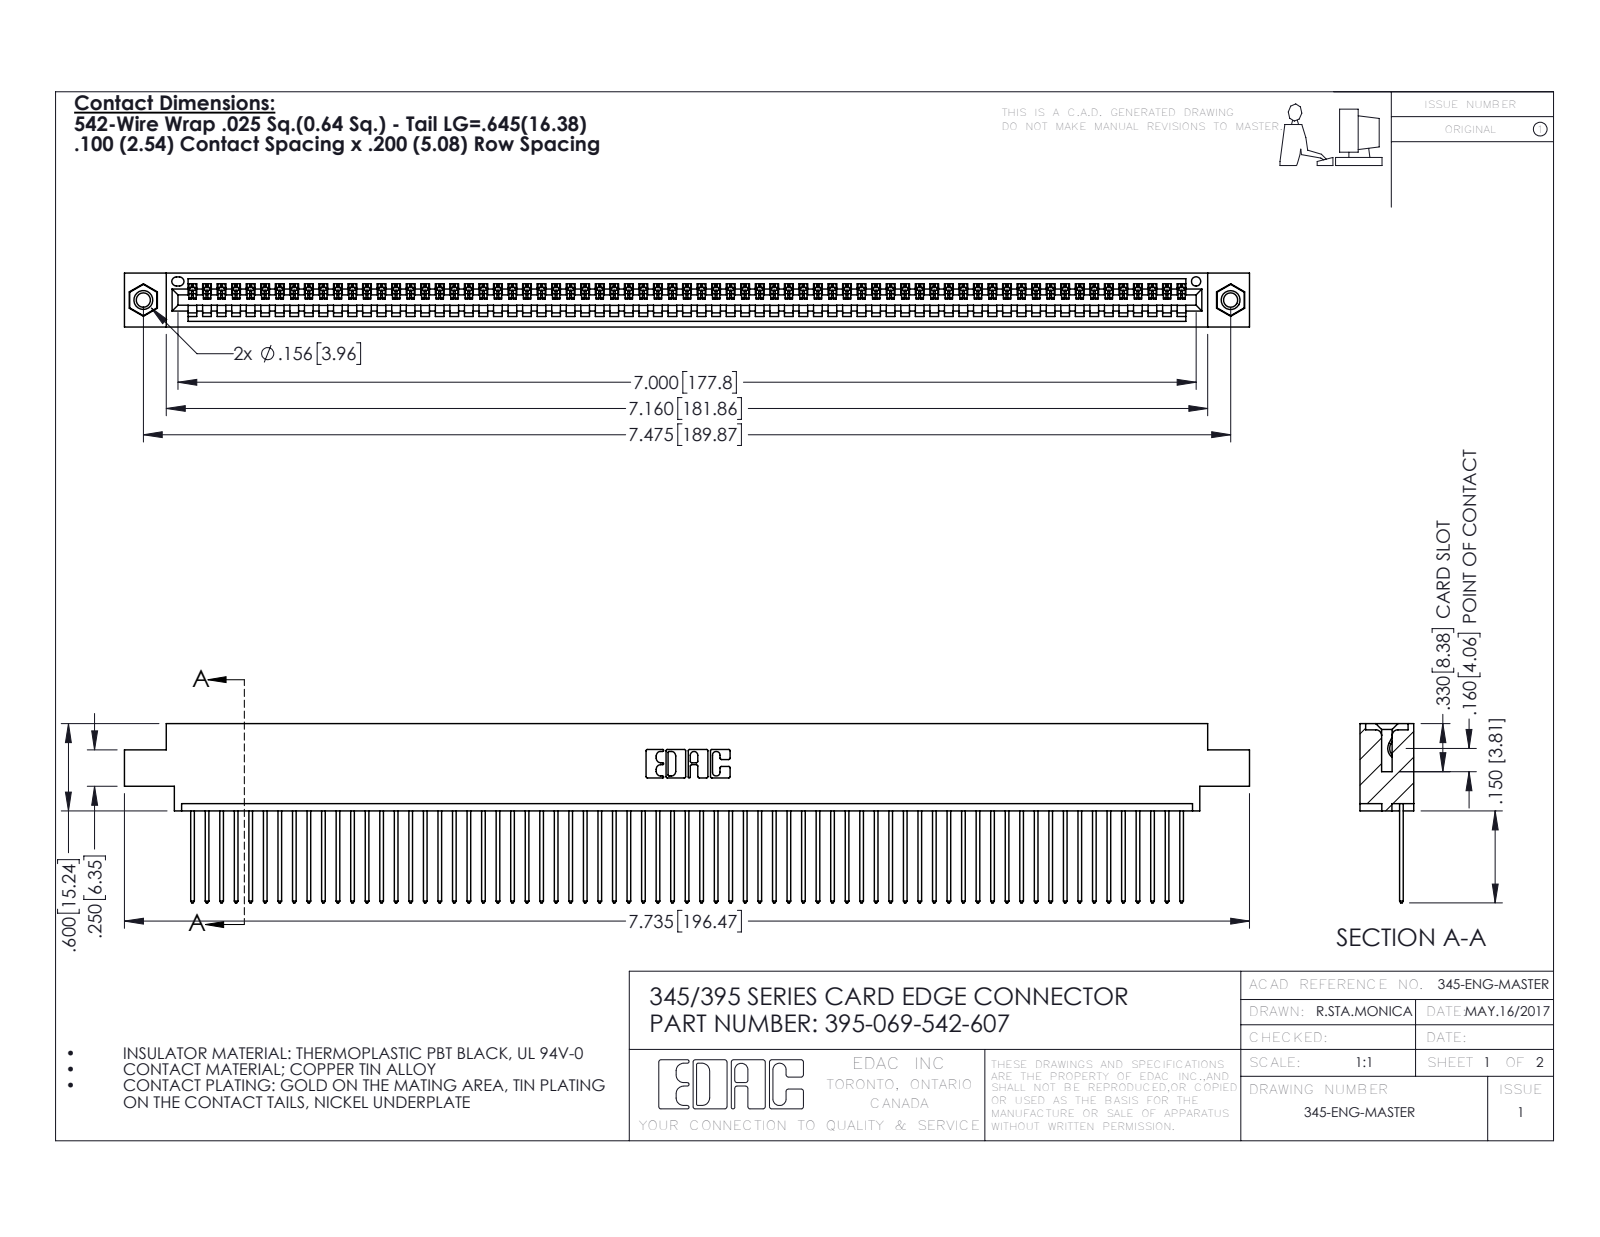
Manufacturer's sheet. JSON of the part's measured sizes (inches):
{"part_name": "395-069-542-607; 345-292-001_345-293-142; 345-250-001_345-250-005-103; 345 Part_0.170 Offset - 0.156 Dia-TI", "step_written_by": "SolidWorks 2016 (CONFIG_CONTROL_DESIGN)", "units": "inches", "bodies": {"solids": 72, "faces": 4192, "planar": 2876, "cylindrical": 1300, "other": 16}, "overall_size": [7.735, 1.232, 0.37], "volume_in3": 1.154, "surface_area_in2": 41.27, "round_holes": [[0.098, 2], [0.125, 2], [0.156, 2], [0.064, 1]], "round_bosses_or_shafts": [[0.155, 2]], "partial_cylinders_radius": [[0.006, 138], [0.01, 138], [0.01, 22], [0.007, 6], [0.031, 6], [0.026, 3], [0.031, 2], [0.04, 2]], "face_to_face_distances": [0.072, 0.298, 0.37, 0.098, 0.272, 0.025, 0.2, 0.225, 0.175, 0.149], "hole_center_spacings": [0.27, 7.239, 7.475]}
